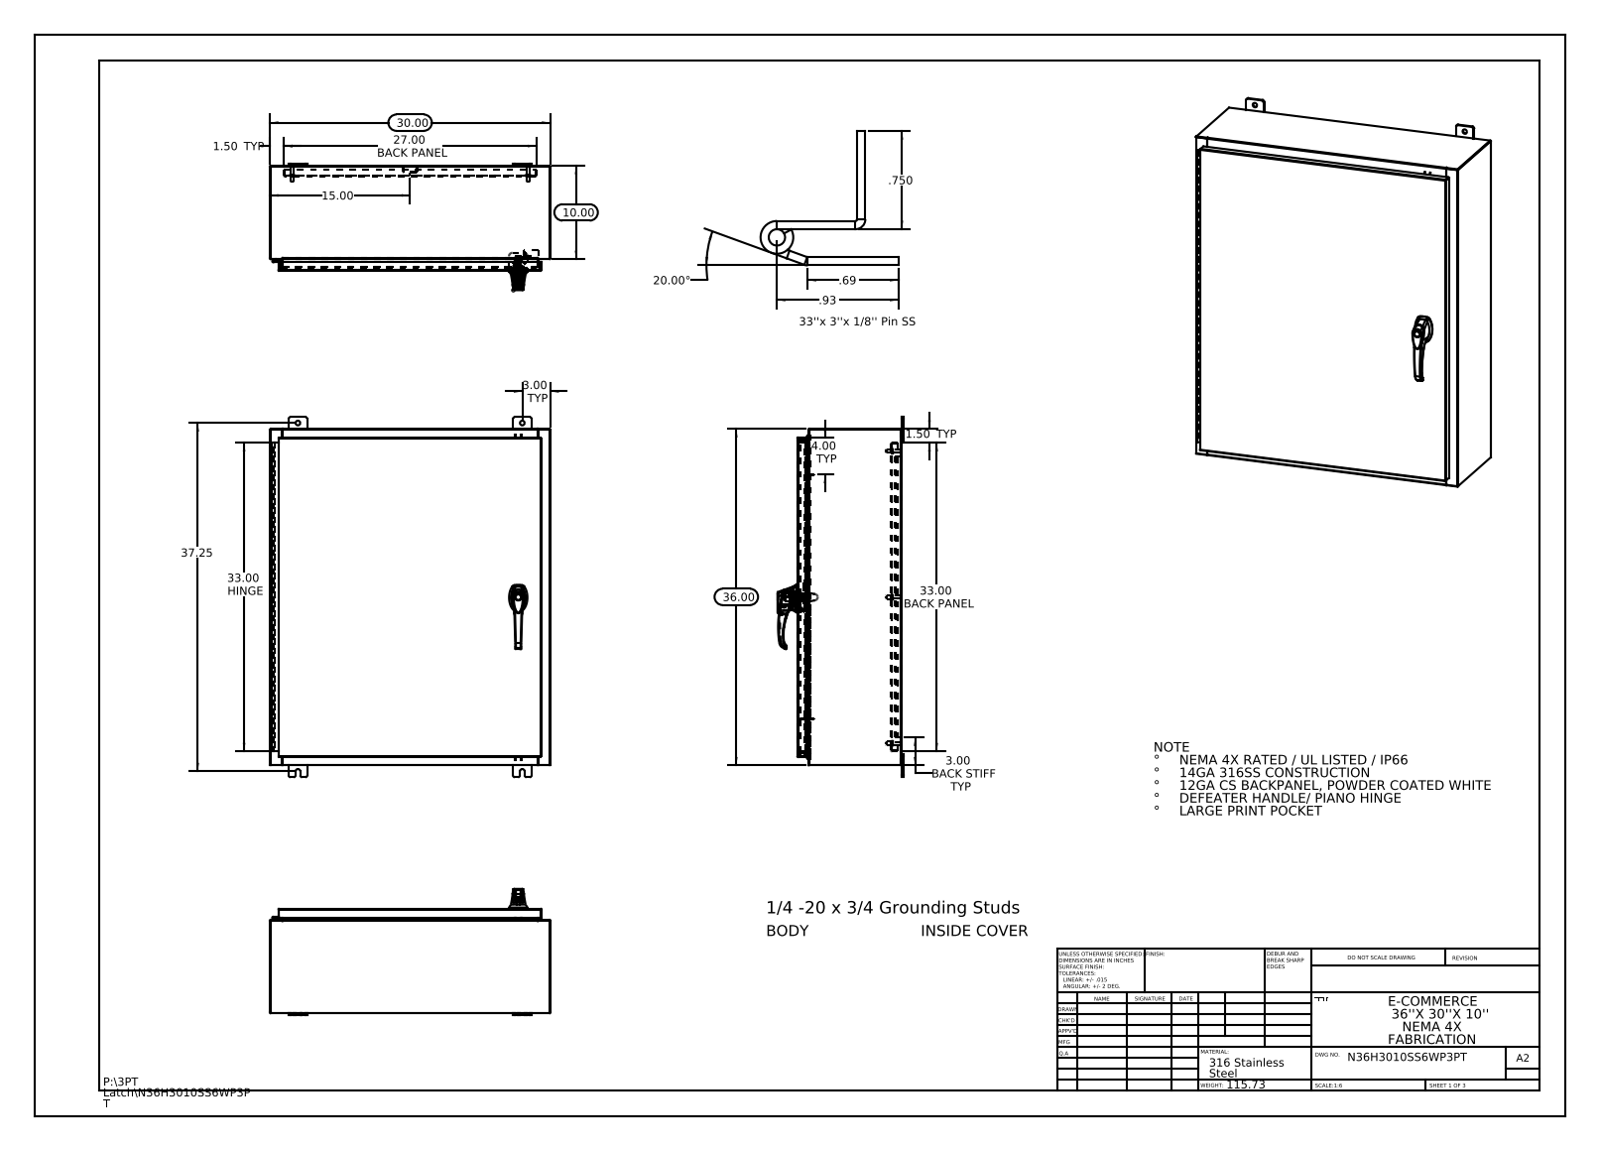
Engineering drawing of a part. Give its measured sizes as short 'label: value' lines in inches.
name: N36H3010SS6WP3PT 263033_Industrilas; N36H3010SS6WP3PT Mounting Studs; N36H3010SS6WP3PT Mounting Feet; 00005309_G26103101 (+8 more)
written by: SolidWorks 2013 (CONFIG_CONTROL_DESIGN)
unit: in
bodies: 34 solids, 2808 faces (1065 planar, 1069 cylindrical, 674 other)
size: 38.5 × 30 × 13.495
volume: 408.9 in³; area: 10 129 in²
holes: 10× ⌀0.5, 4× ⌀0.25, 3× ⌀0.138, 3× ⌀0.161, 2× ⌀0.079, 2× ⌀0.203, 2× ⌀0.313, 2× ⌀0.437, 1× ⌀0.125, 1× ⌀0.125, 1× ⌀0.197, 1× ⌀0.276
bosses: 6× ⌀0.625, 6× ⌀0.375, 6× ⌀0.33, 1× ⌀1.181, 1× ⌀0.748, 1× ⌀0.68, 1× ⌀0.661, 1× ⌀0.639
rounds: 37× R0.118, 33× R0.006, 28× R0.013, 24× R0.19, 22× R0.088, 15× R0.039, 12× R0.028, 6× R0.008
face distances: 0.075, 11.126, 11.051, 0.104, 11.201, 1, 10.126, 1.075, 10.051, 1.179
hole spacings: 11.363, 13.669, 15.625, 29.694, 25.25, 28.129, 0.295, 0.625
